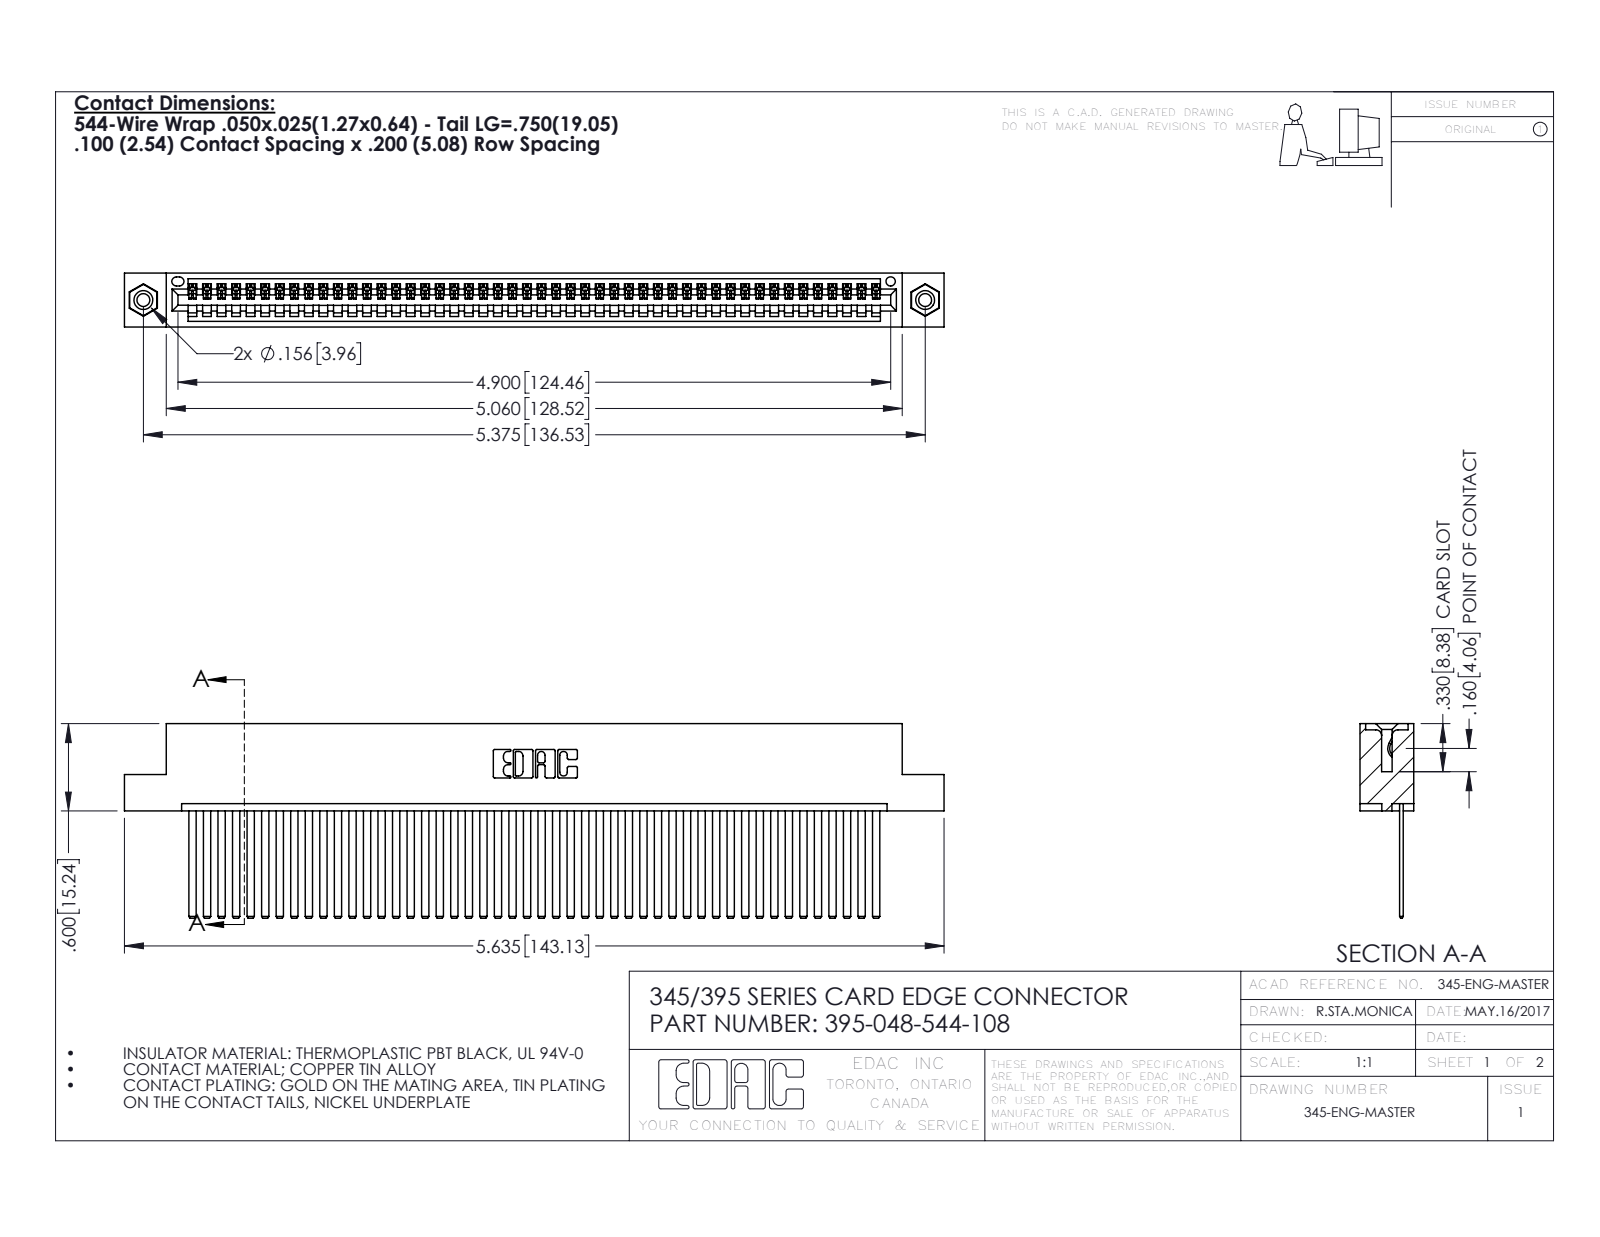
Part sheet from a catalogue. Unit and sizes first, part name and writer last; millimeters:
Units: millimetres
Overall size (bounding box): 143.1 × 34 × 9.4
Round holes (diameter × count): ⌀2.3 ×2, ⌀3.2 ×2, ⌀4 ×2, ⌀1.6 ×1
Round bosses / shafts (diameter × count): ⌀3.9 ×2
Partial cylindrical surfaces — rounded edges, fillets, slot ends (radius × count): R0.2 ×96, R0.3 ×22, R0.2 ×6, R0.8 ×6, R0.7 ×3, R0.8 ×2, R1 ×2, R0.4 ×1
Main face-to-face distances: 1.8, 7.6, 0.6, 2.5, 6.9, 9.4, 5.1, 5.7, 3.8, 1.8
Hole centre spacings: 6.9, 130.5, 136.5
Volume: 14 200 mm³ · Surface area: 20 630 mm²
Bodies: 51 solids, 2682 faces (1840 planar, 826 cylindrical, 16 other)
Part name (STEP PRODUCT): 345 Part_Flush Mounting Lugs - 0.156 Dia-TI; 395-048-544-108; 345-250-001_345-250-003-102; 345-292-001_345-293-144
STEP written by: SolidWorks 2016 (CONFIG_CONTROL_DESIGN)
